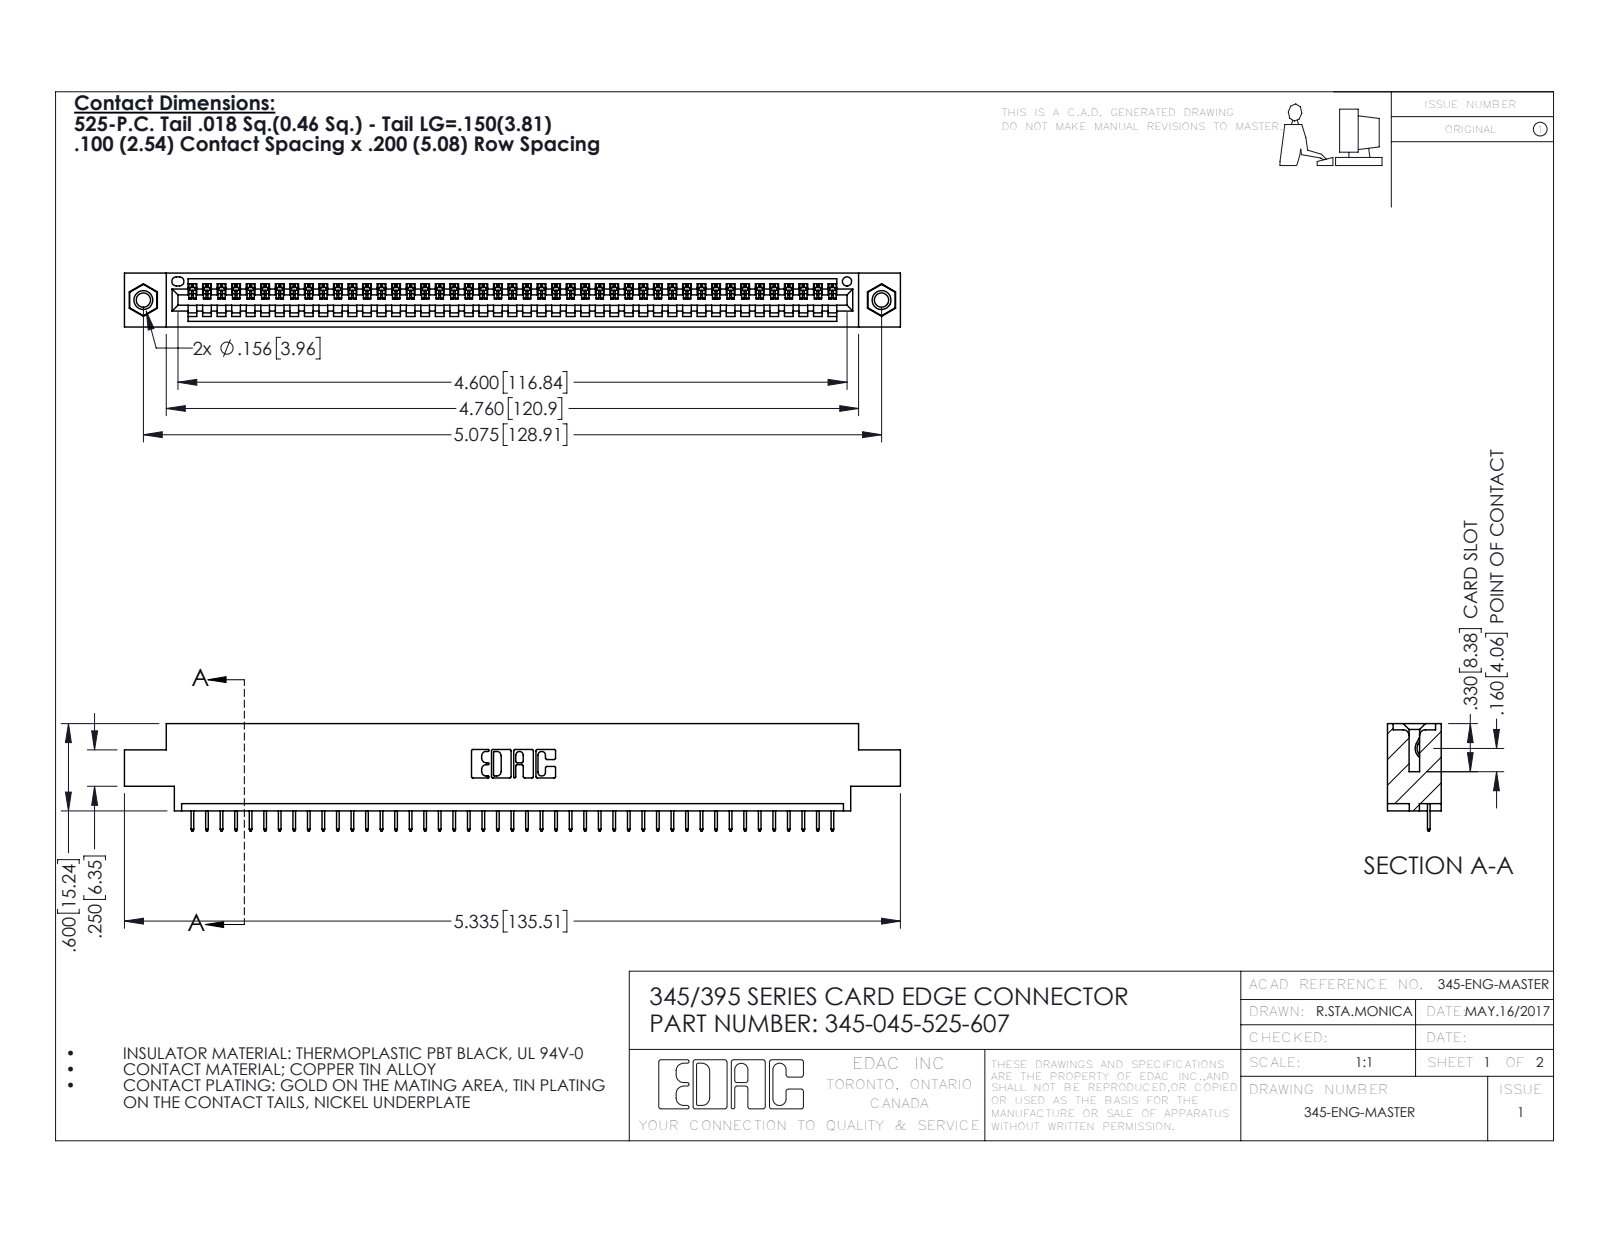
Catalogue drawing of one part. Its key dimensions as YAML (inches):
part_name: "345-045-525-607; 345-292-001_345-293-125; 345-250-001_345-250-005-103; 345 Part_0.170 Offset - 0.156 Dia-TI"
step_written_by: "SolidWorks 2020 (CONFIG_CONTROL_DESIGN)"
units: inches
bodies: {solids: 48, faces: 2980, planar: 2186, cylindrical: 778, other: 16}
overall_size: [5.335, 0.737, 0.37]
volume: 0.768
surface_area: 25.28
round_holes:
  - {diameter: 0.098, count: 2}
  - {diameter: 0.125, count: 2}
  - {diameter: 0.156, count: 2}
  - {diameter: 0.064, count: 1}
round_bosses_or_shafts:
  - {diameter: 0.155, count: 2}
partial_cylinders:
  - {radius: 0.006, count: 90}
  - {radius: 0.01, count: 22}
  - {radius: 0.007, count: 6}
  - {radius: 0.031, count: 6}
  - {radius: 0.026, count: 3}
  - {radius: 0.031, count: 2}
  - {radius: 0.04, count: 2}
  - {radius: 0.014, count: 1}
face_to_face_distances: [0.072, 0.298, 0.37, 0.2, 0.098, 0.272, 0.025, 0.225, 0.072, 0.175]
hole_center_spacings: [0.27, 4.839, 5.075]
